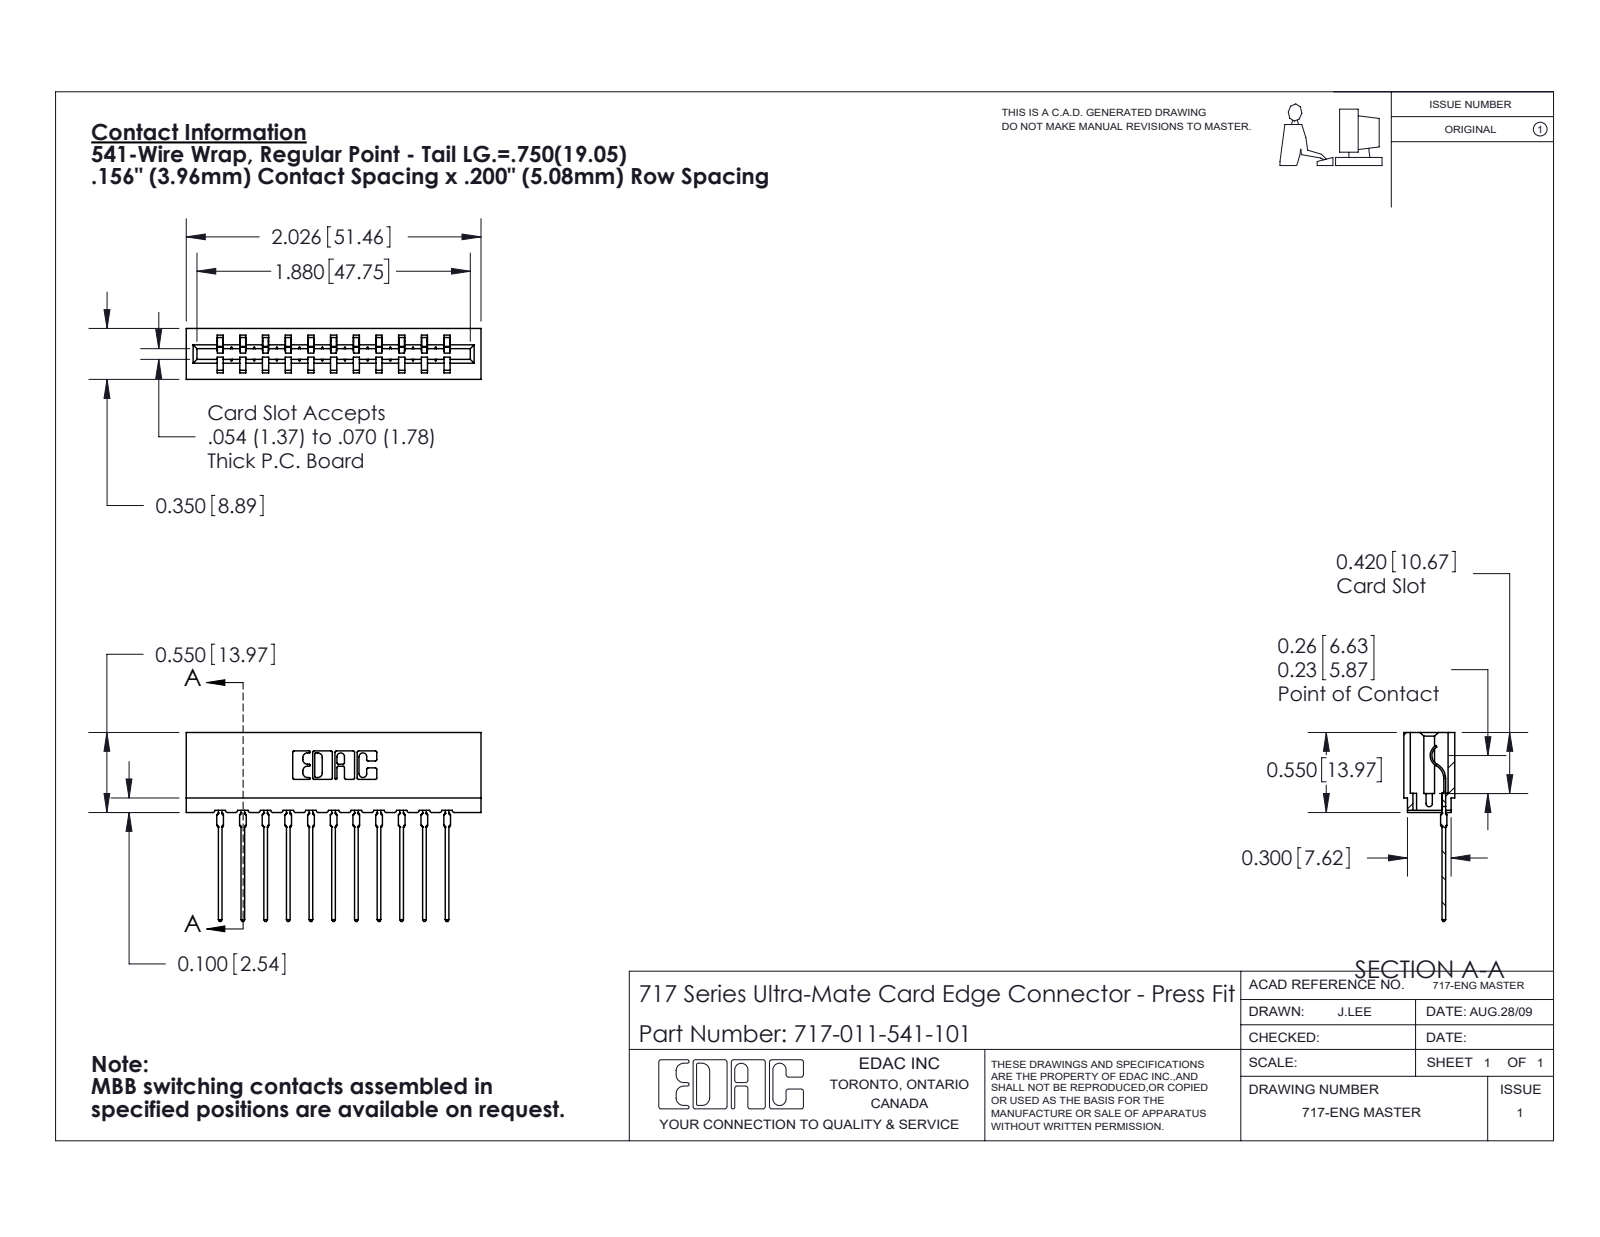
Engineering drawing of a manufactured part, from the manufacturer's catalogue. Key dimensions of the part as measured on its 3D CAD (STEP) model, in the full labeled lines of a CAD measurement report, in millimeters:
Part name (STEP PRODUCT): 717-011-541-101; 745-292-001_541; 717 Part_Insulator Option - 06
STEP written by: SolidWorks 2020 (CONFIG_CONTROL_DESIGN)
Units: millimetres
Bodies: 12 solids, 1337 faces (802 planar, 249 cylindrical, 286 other)
Overall size (bounding box): 51.5 × 33 × 8.9
Volume: 4 540 mm³ · Surface area: 6 262 mm²
Partial cylindrical surfaces — rounded edges, fillets, slot ends (radius × count): R0.3 ×22, R0.4 ×22, R0.5 ×22, R0.2 ×6, R0.8 ×6, R0.1 ×4, R0.3 ×4, R0.7 ×3
Main face-to-face distances: 5.4, 4, 3.5, 11.9, 15.8, 8.9, 7.9, 5, 7.9, 1.1
